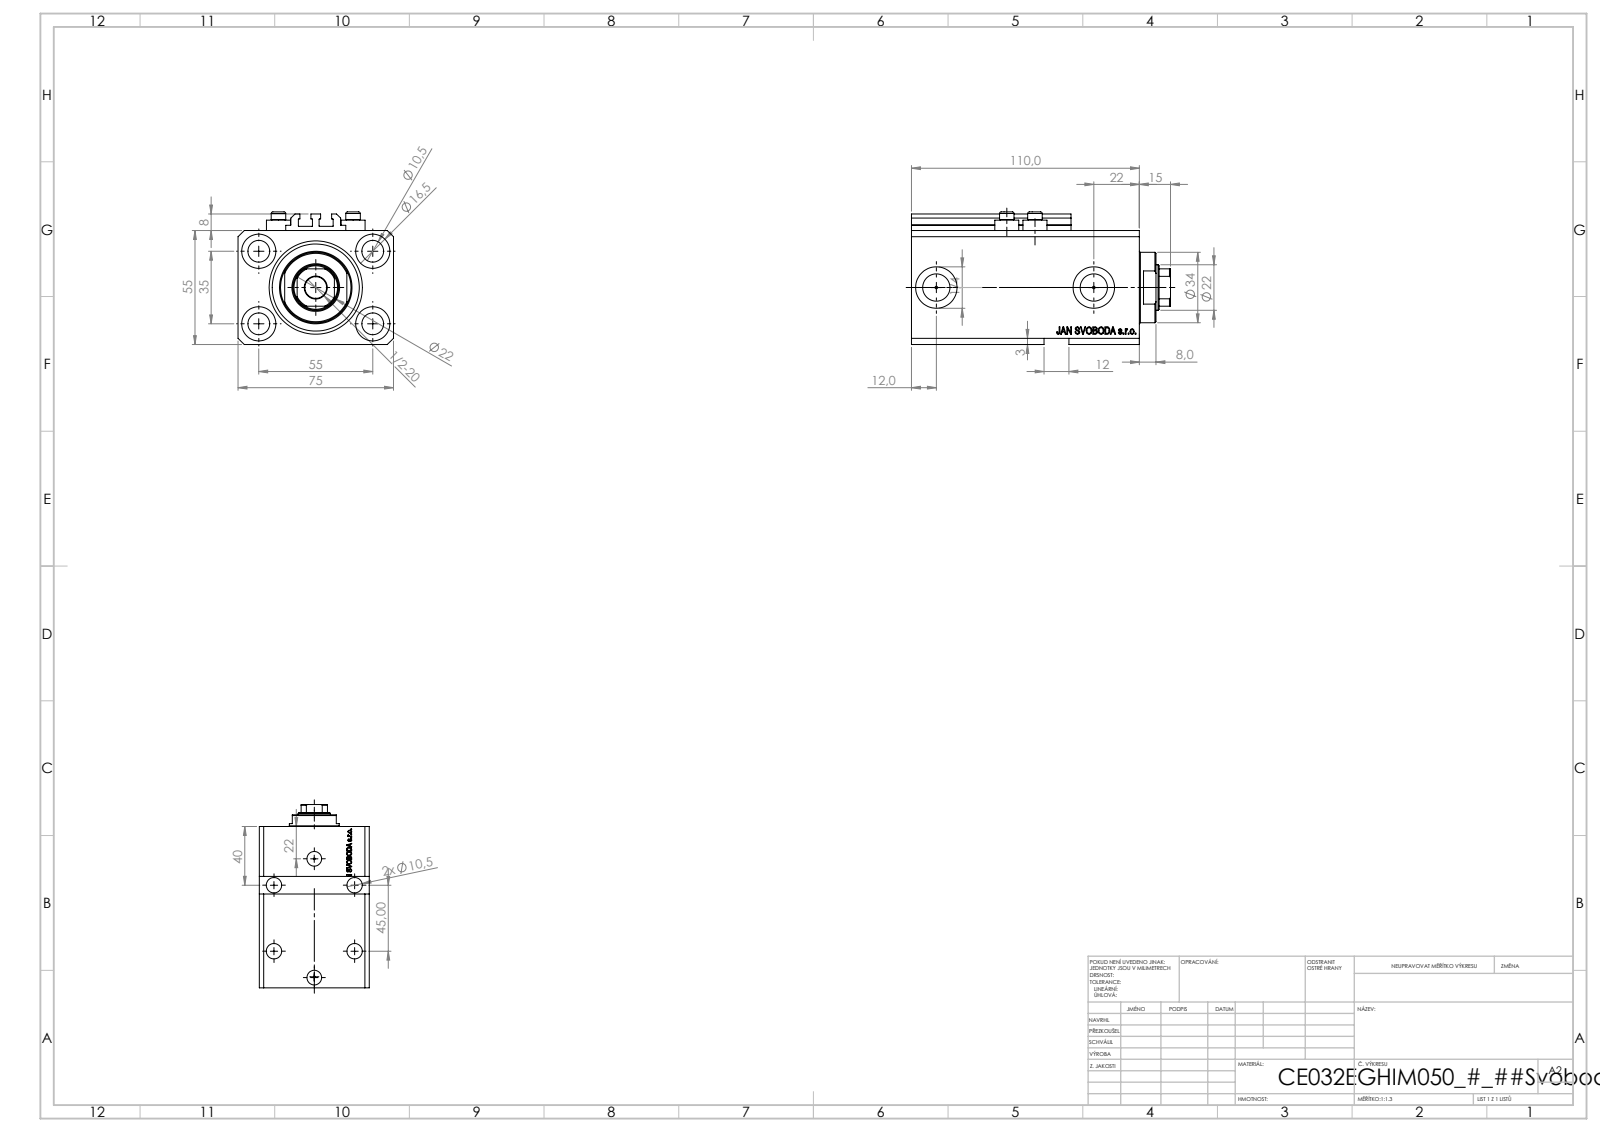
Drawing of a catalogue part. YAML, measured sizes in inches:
part_name: "V250CE_VC_E; ALLEN BOLT V250CE; V250CE_C_VCP; V250CE_E_Body"
step_written_by: "SolidWorks 2019 (CONFIG_CONTROL_DESIGN)"
units: inches
bodies: {solids: 8, faces: 1084, planar: 514, cylindrical: 146, other: 424}
overall_size: [4.921, 2.953, 2.52]
volume: 23.27
surface_area: 148.2
round_holes:
  - {diameter: 0.413, count: 9}
  - {diameter: 0.049, count: 4}
  - {diameter: 0.157, count: 4}
  - {diameter: 0.65, count: 4}
  - {diameter: 0.394, count: 2}
  - {diameter: 0.518, count: 2}
  - {diameter: 0.787, count: 2}
  - {diameter: 0.866, count: 1}
  - {diameter: 1.26, count: 1}
  - {diameter: 1.772, count: 1}
round_bosses_or_shafts:
  - {diameter: 0.457, count: 4}
  - {diameter: 0.276, count: 4}
  - {diameter: 1.339, count: 1}
partial_cylinders:
  - {radius: 0.008, count: 10}
  - {radius: 0.413, count: 1}
face_to_face_distances: [2.165, 2.953, 0.591, 4.331, 3.74, 0.118, 0.39, 3.35, 3.941, 2.244]
hole_center_spacings: [1.283, 1.294, 2.165, 2.706, 0.535, 0.555, 0.907, 1.016]
